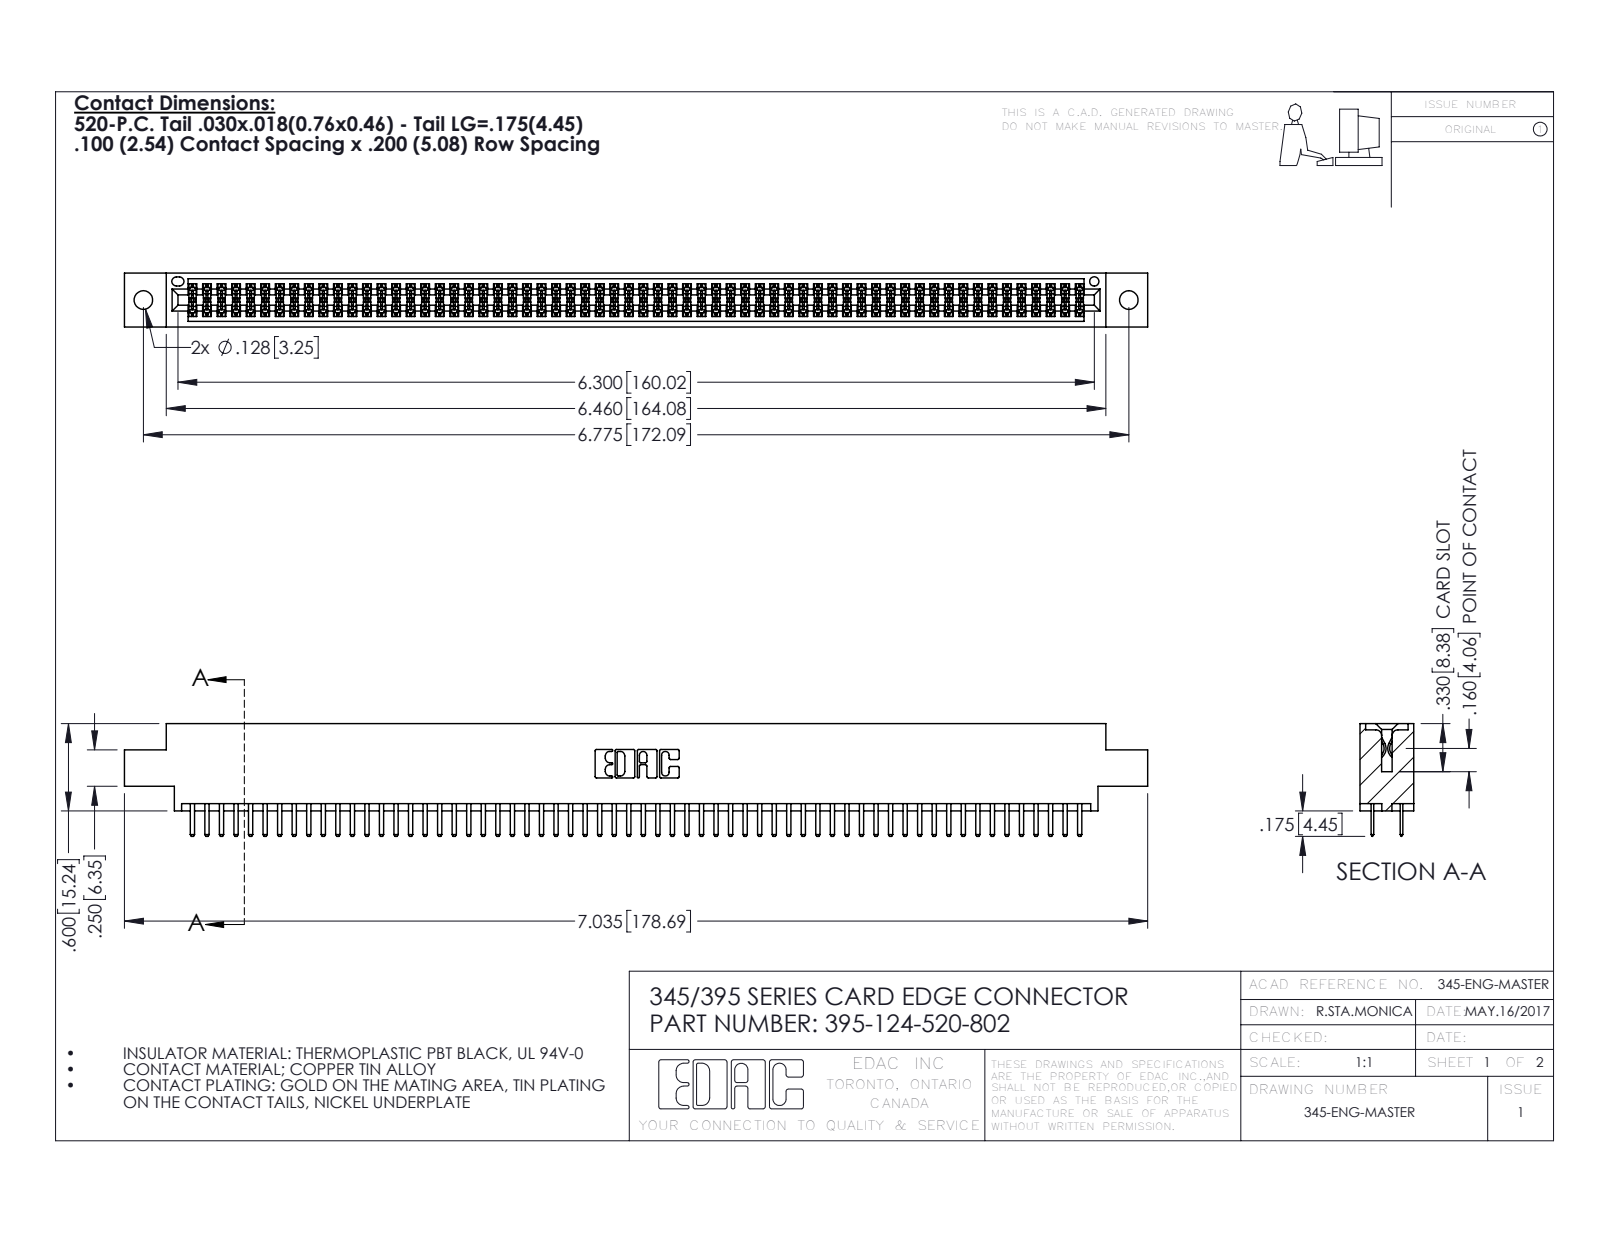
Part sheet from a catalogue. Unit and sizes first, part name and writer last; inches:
Units: inches
Overall size (bounding box): 7.035 × 0.775 × 0.37
Round holes (diameter × count): ⌀0.128 ×2, ⌀0.064 ×1
Partial cylindrical surfaces — rounded edges, fillets, slot ends (radius × count): R0.006 ×186, R0.01 ×128, R0.01 ×22, R0.007 ×6, R0.031 ×6, R0.026 ×3, R0.014 ×2, R0.019 ×2
Main face-to-face distances: 0.072, 0.298, 0.2, 0.37, 0.098, 0.272, 0.025, 0.225, 0.022, 0.072
Hole centre spacings: 0.27, 6.539, 6.775
Volume: 1.058 in³ · Surface area: 39.95 in²
Bodies: 125 solids, 6826 faces (4424 planar, 2402 cylindrical, 0 other)
Part name (STEP PRODUCT): 395-124-520-802; 345-292-001_345-293-120; 345 Part_0.170 Offset - 0.128 Dia
STEP written by: SolidWorks 2016 (CONFIG_CONTROL_DESIGN)
